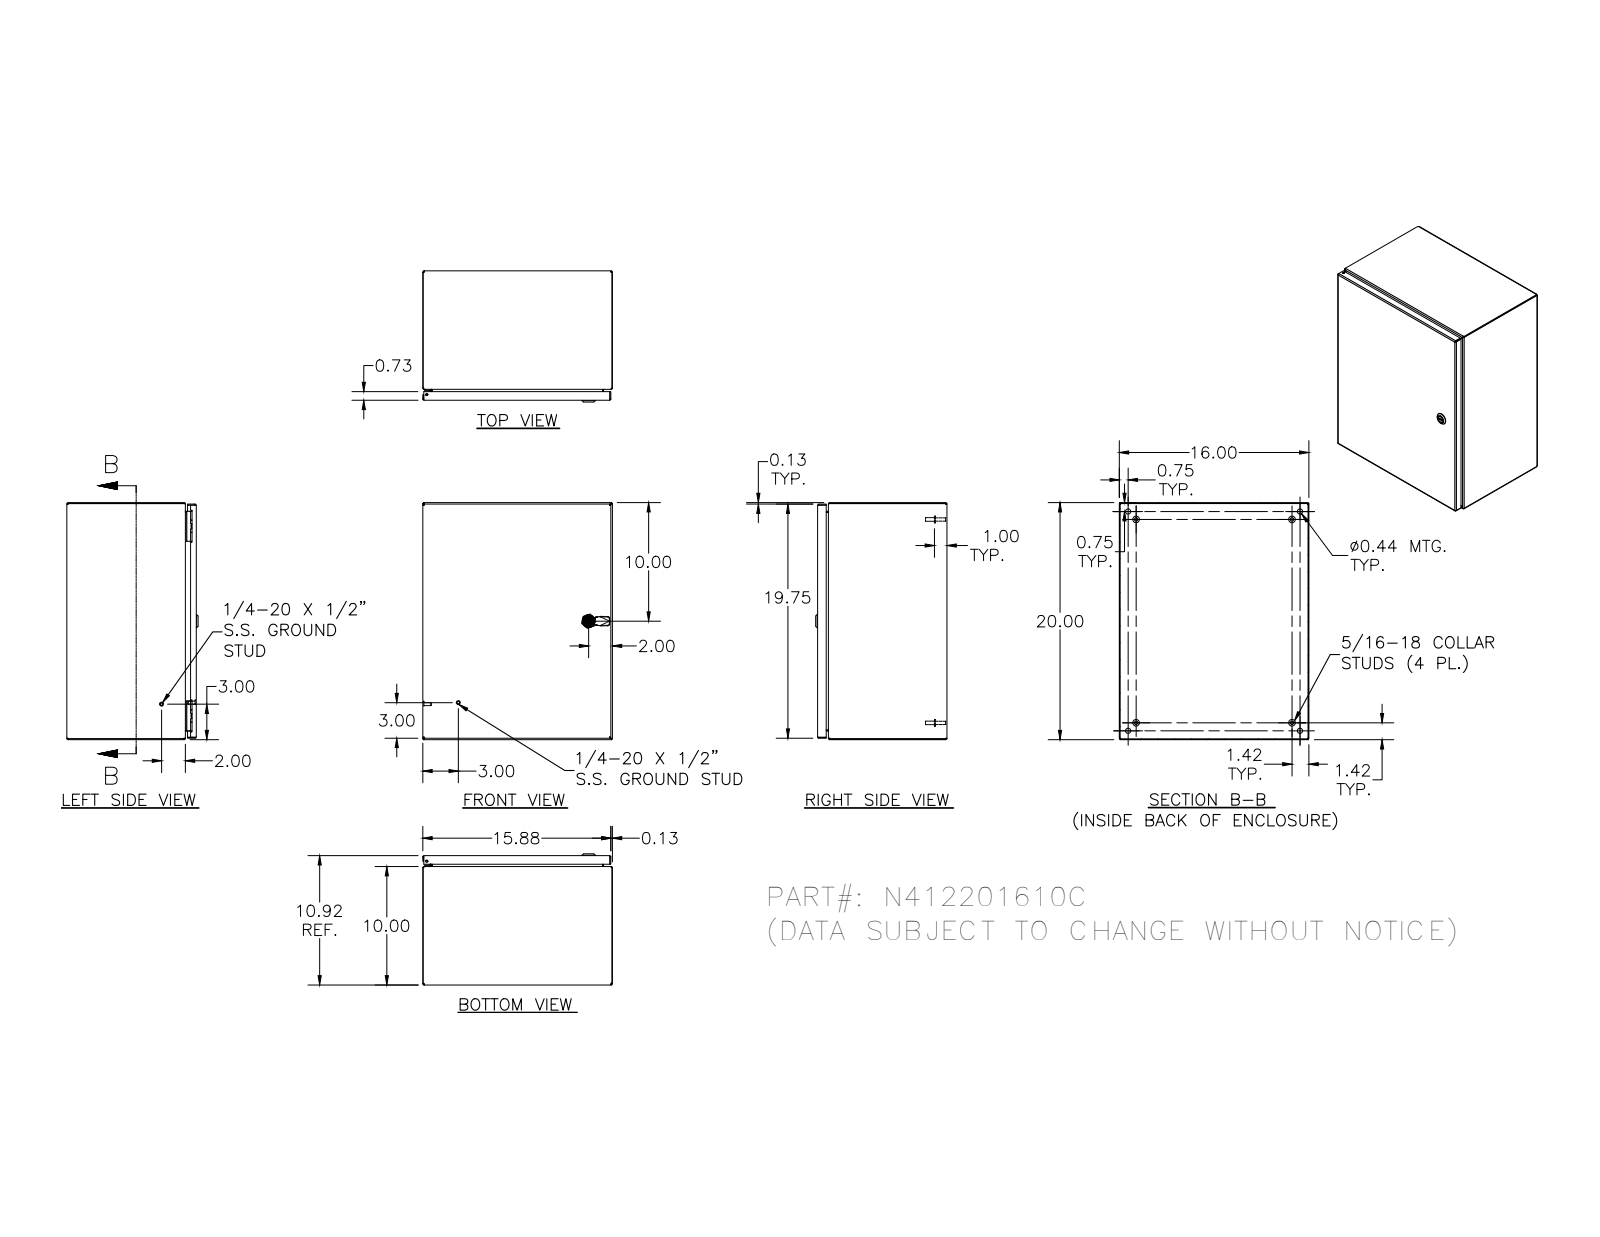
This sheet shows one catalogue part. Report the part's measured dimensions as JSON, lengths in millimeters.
{"part_name": "N412201610C", "step_written_by": "SolidWorks 2018 (AUTOMOTIVE_DESIGN)", "units": "millimeters", "bodies": {"solids": 33, "faces": 1449, "planar": 530, "cylindrical": 547, "other": 372}, "overall_size": [508, 406.4, 281.3], "volume_mm3": 1829000, "surface_area_mm2": 1957000, "round_holes": [[4.8, 5], [2.4, 4], [3.9, 4], [4.2, 4], [4.4, 4], [11.1, 4], [4, 2], [4.7, 1], [5, 1], [8, 1], [10, 1], [10.2, 1]], "round_bosses_or_shafts": [[6.4, 10], [3.3, 5], [14.3, 4], [9.1, 4], [8.1, 4], [7.6, 4], [7, 4], [6.5, 4]], "partial_cylinders_radius": [[0.3, 30], [0.8, 30], [1.3, 26], [2.7, 20], [0.4, 18], [3.2, 16], [0.5, 13], [0.8, 8]], "face_to_face_distances": [1.9, 275.4, 1.9, 273.5, 277.3, 404.5, 406.4, 402.6, 404.5, 506.1], "hole_center_spacings": [406.4, 16.8, 16.7, 33.2, 49.9, 389.6, 406.3, 423.1]}
